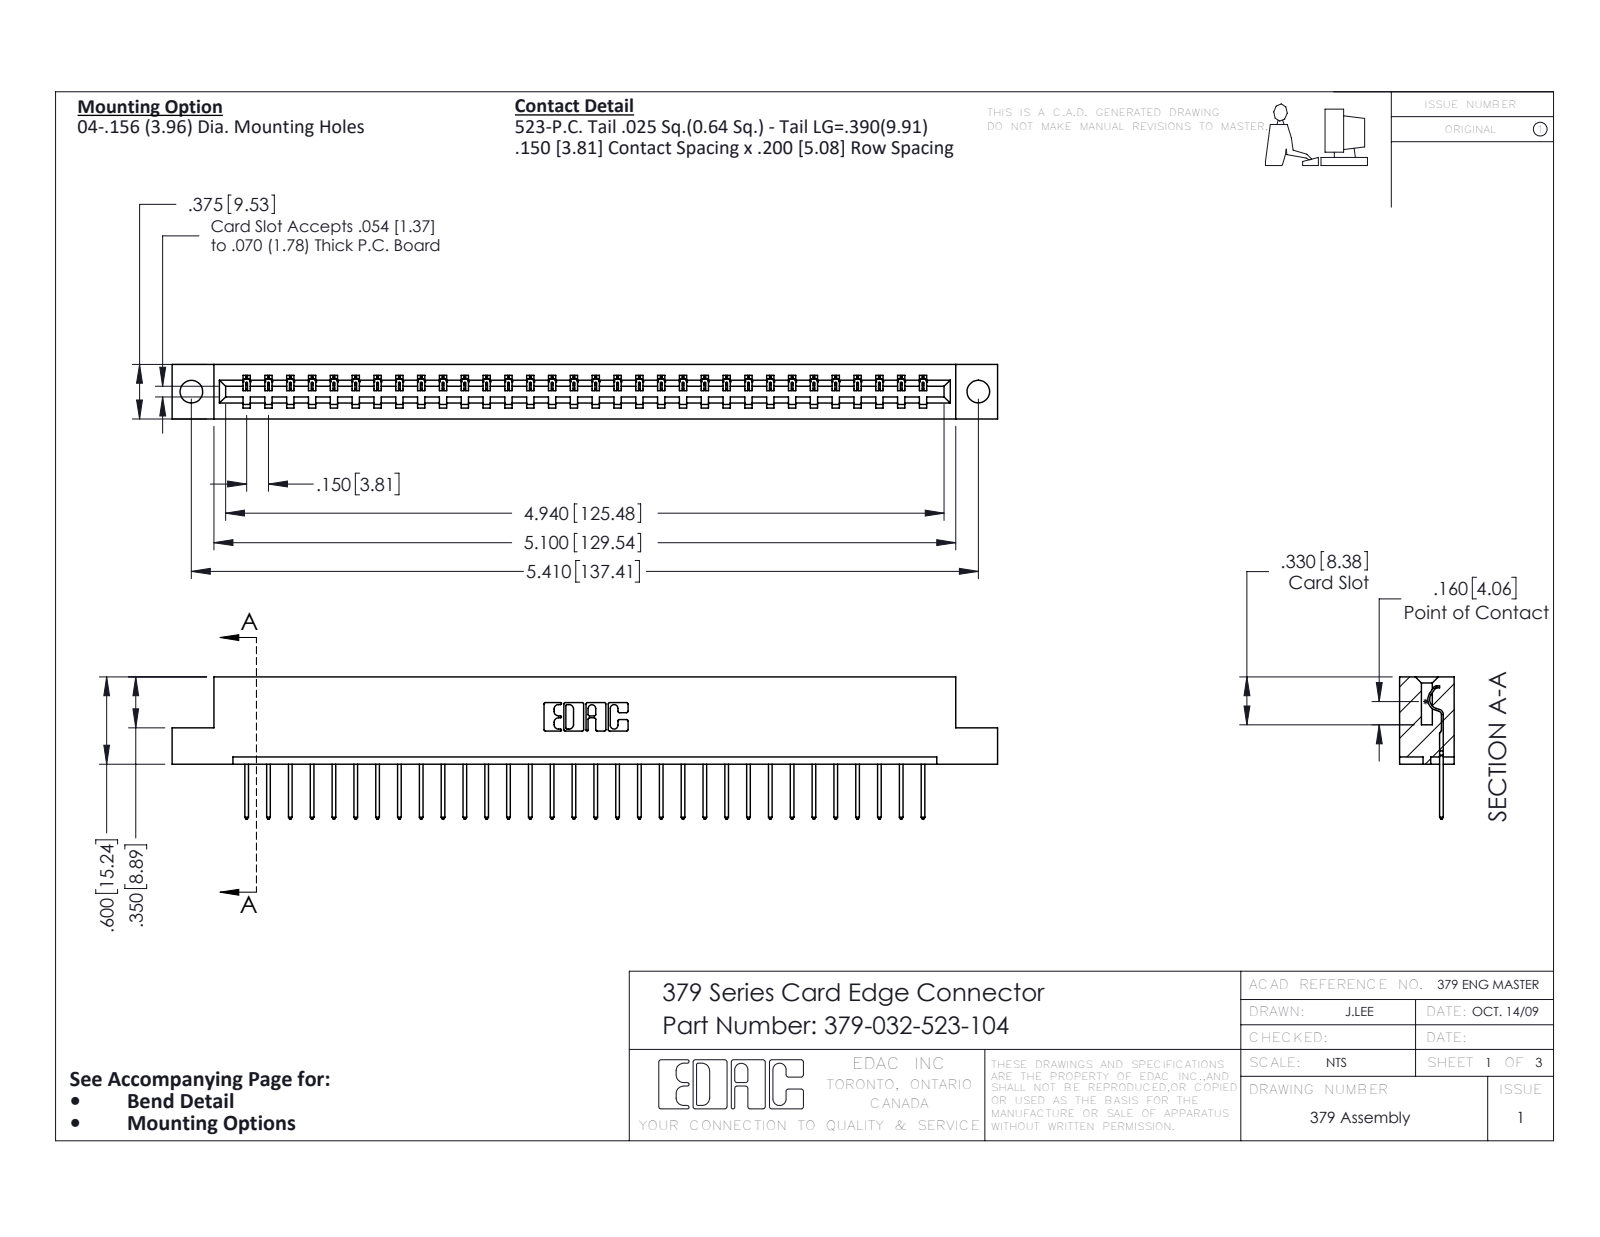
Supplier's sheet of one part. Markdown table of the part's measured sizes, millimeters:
| quantity | value |
| --- | --- |
| part name | 379-032-523-104; 379 Part_Flush - .156 Dia - TH; 345-292-001_345-293-123 |
| STEP written by | SolidWorks 2016 (CONFIG_CONTROL_DESIGN) |
| units | millimeters |
| bodies | 33 solids, 1970 faces (1414 planar, 556 cylindrical, 0 other) |
| overall size | 144.1 × 24.8 × 9.5 |
| volume | 14 900 mm³ |
| surface area | 15 050 mm² |
| round holes (diameter × count) | 4 × 2 |
| partial cylindrical surfaces (radius × count) | 0.2 × 64, 0.3 × 64, 0.3 × 22, 0.2 × 6, 0.8 × 6, 0.7 × 3, 0.4 × 1, 0.6 × 1 |
| main face-to-face distances | 7.6, 1.9, 9.5, 5.7, 5.1, 15.2, 7, 2.5, 0.6, 14 |
| hole center spacings | 137.4 |
